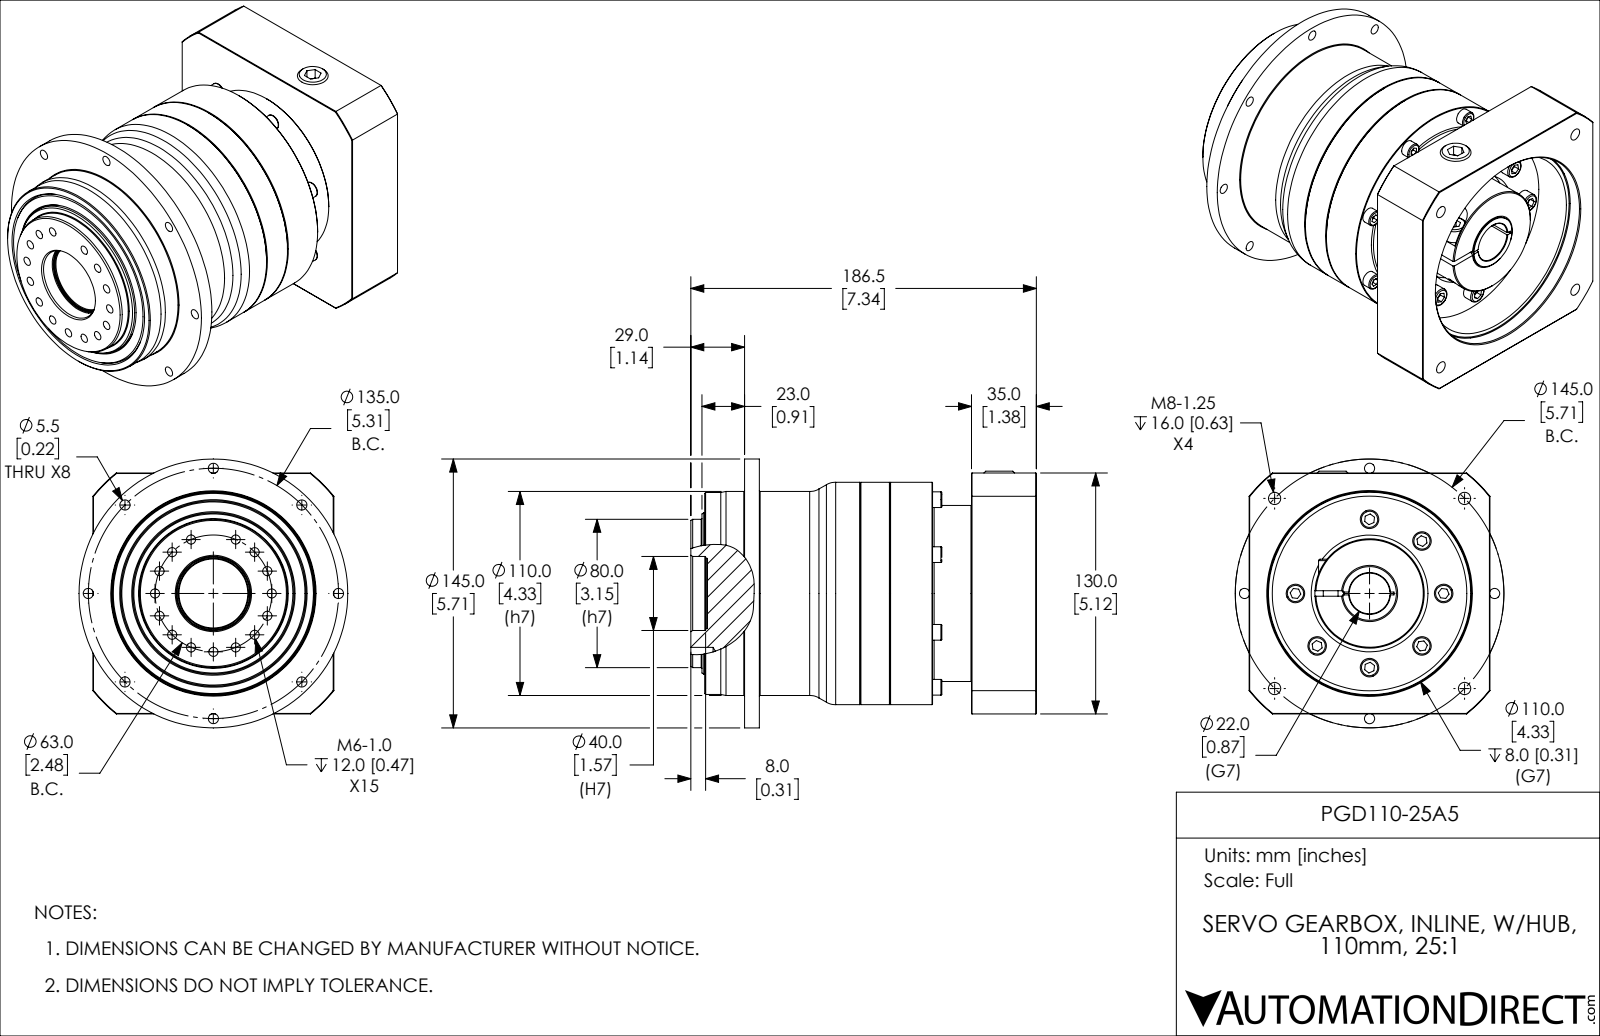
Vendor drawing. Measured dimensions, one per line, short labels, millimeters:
name: PGD110-25A5
written by: SolidWorks 2015 (AUTOMOTIVE_DESIGN)
unit: mm
bodies: 11 solids, 578 faces (302 planar, 193 cylindrical, 83 other)
size: 186.5 × 145 × 145
volume: 1 810 000 mm³; area: 169 611 mm²
holes: 11× ⌀4.92, 8× ⌀5.5, 4× ⌀4.92, 3× ⌀6.65, 2× ⌀8, 1× ⌀6.65, 1× ⌀8.8, 1× ⌀13, 1× ⌀15, 1× ⌀28, 1× ⌀37.2, 1× ⌀39.2
bosses: 7× ⌀10, 1× ⌀145, 1× ⌀120, 1× ⌀111, 1× ⌀110, 1× ⌀95, 1× ⌀80, 1× ⌀54.5
rounds: 7× R4.25, 1× R7, 1× R83.2
face distances: 157.5, 4, 144.5, 29, 22, 129.4, 6, 122.5, 118.5, 26
hole spacings: 40.25, 62.62, 84.71, 97.35, 12.29, 52.38, 74.49, 44.54
